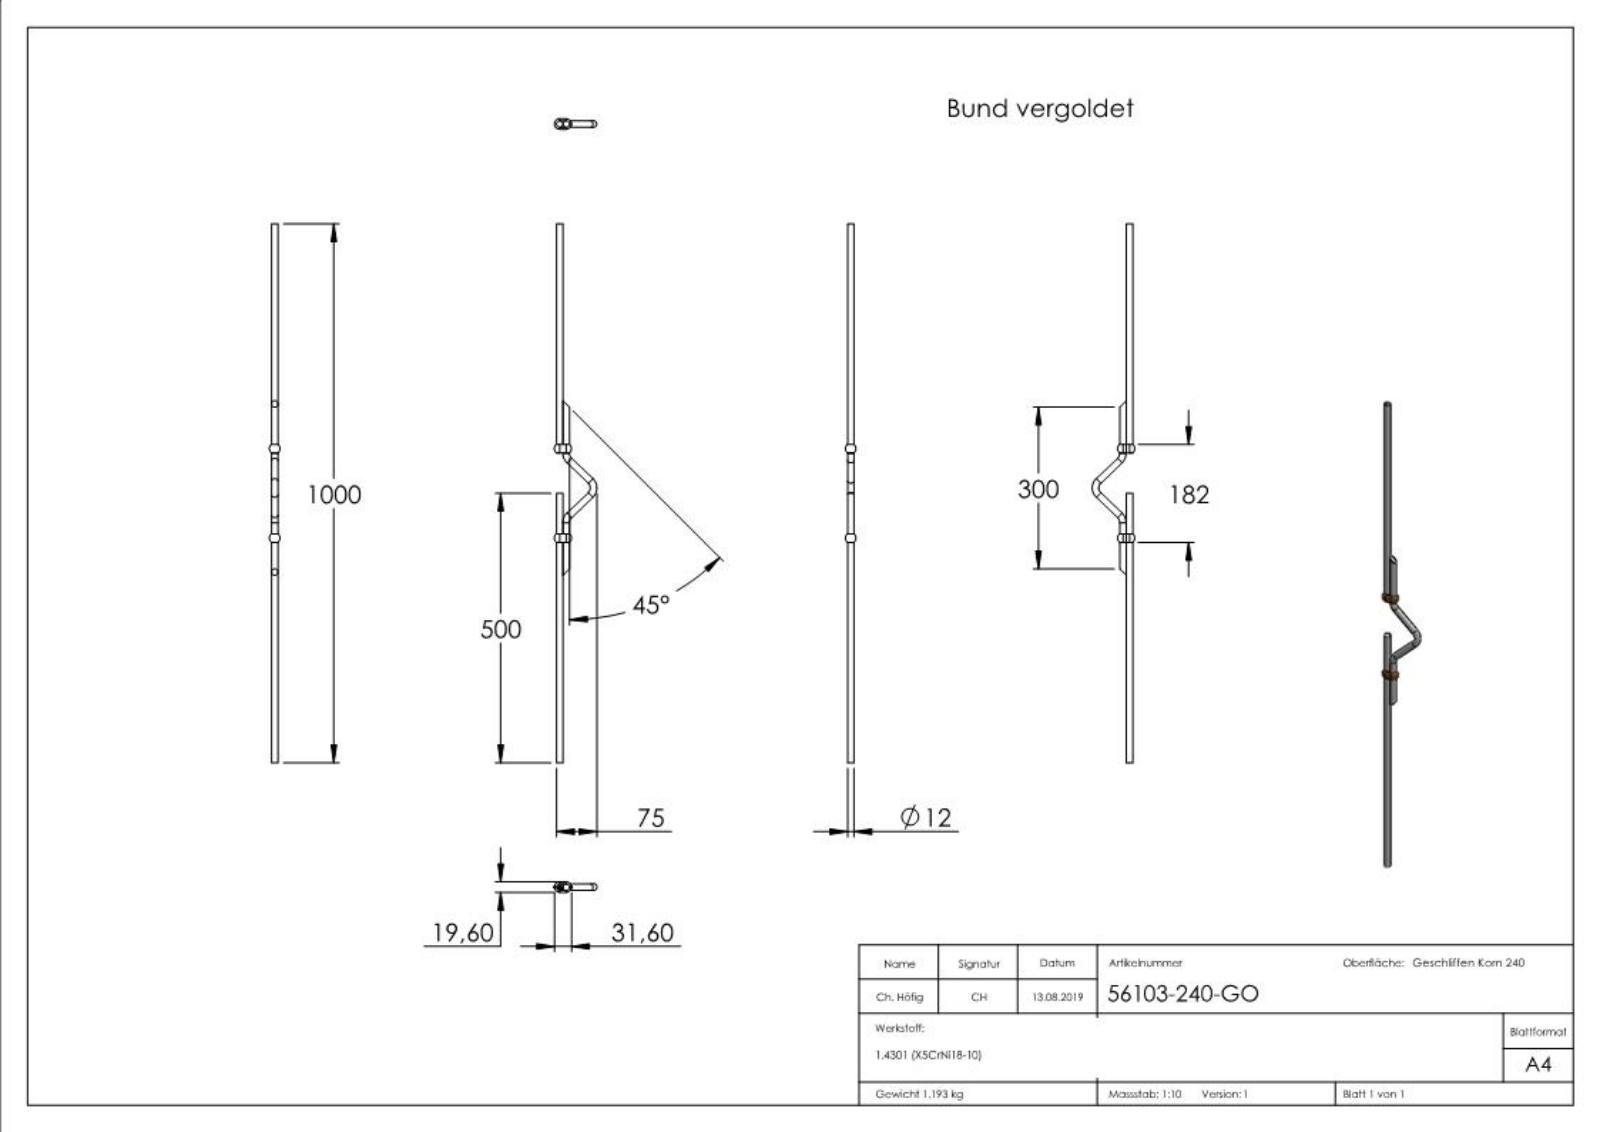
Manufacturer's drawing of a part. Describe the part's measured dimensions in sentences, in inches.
The part is named "56103-240-GO". Its 3-D file was written by "SolidWorks 2015 (CONFIG_CONTROL_DESIGN)". It is 5 solids with 299 faces: 143 planar, 24 cylindrical and 132 other. Overall it measures 39.37 by 2.953 by 0.772 inches. Its volume is 9.183 cubic inches and its surface area 83.29 square inches. Round bosses or shafts: 4 of diameter 0.472. Partial cylindrical surfaces (rounded edges, fillets, slot ends): 4 of radius 0.406. The main face-to-face distances are 0.472, 19.685, 2.953, 22.638, 39.37, 16.732, 39.366, 19.681, 16.728, 0.07.
